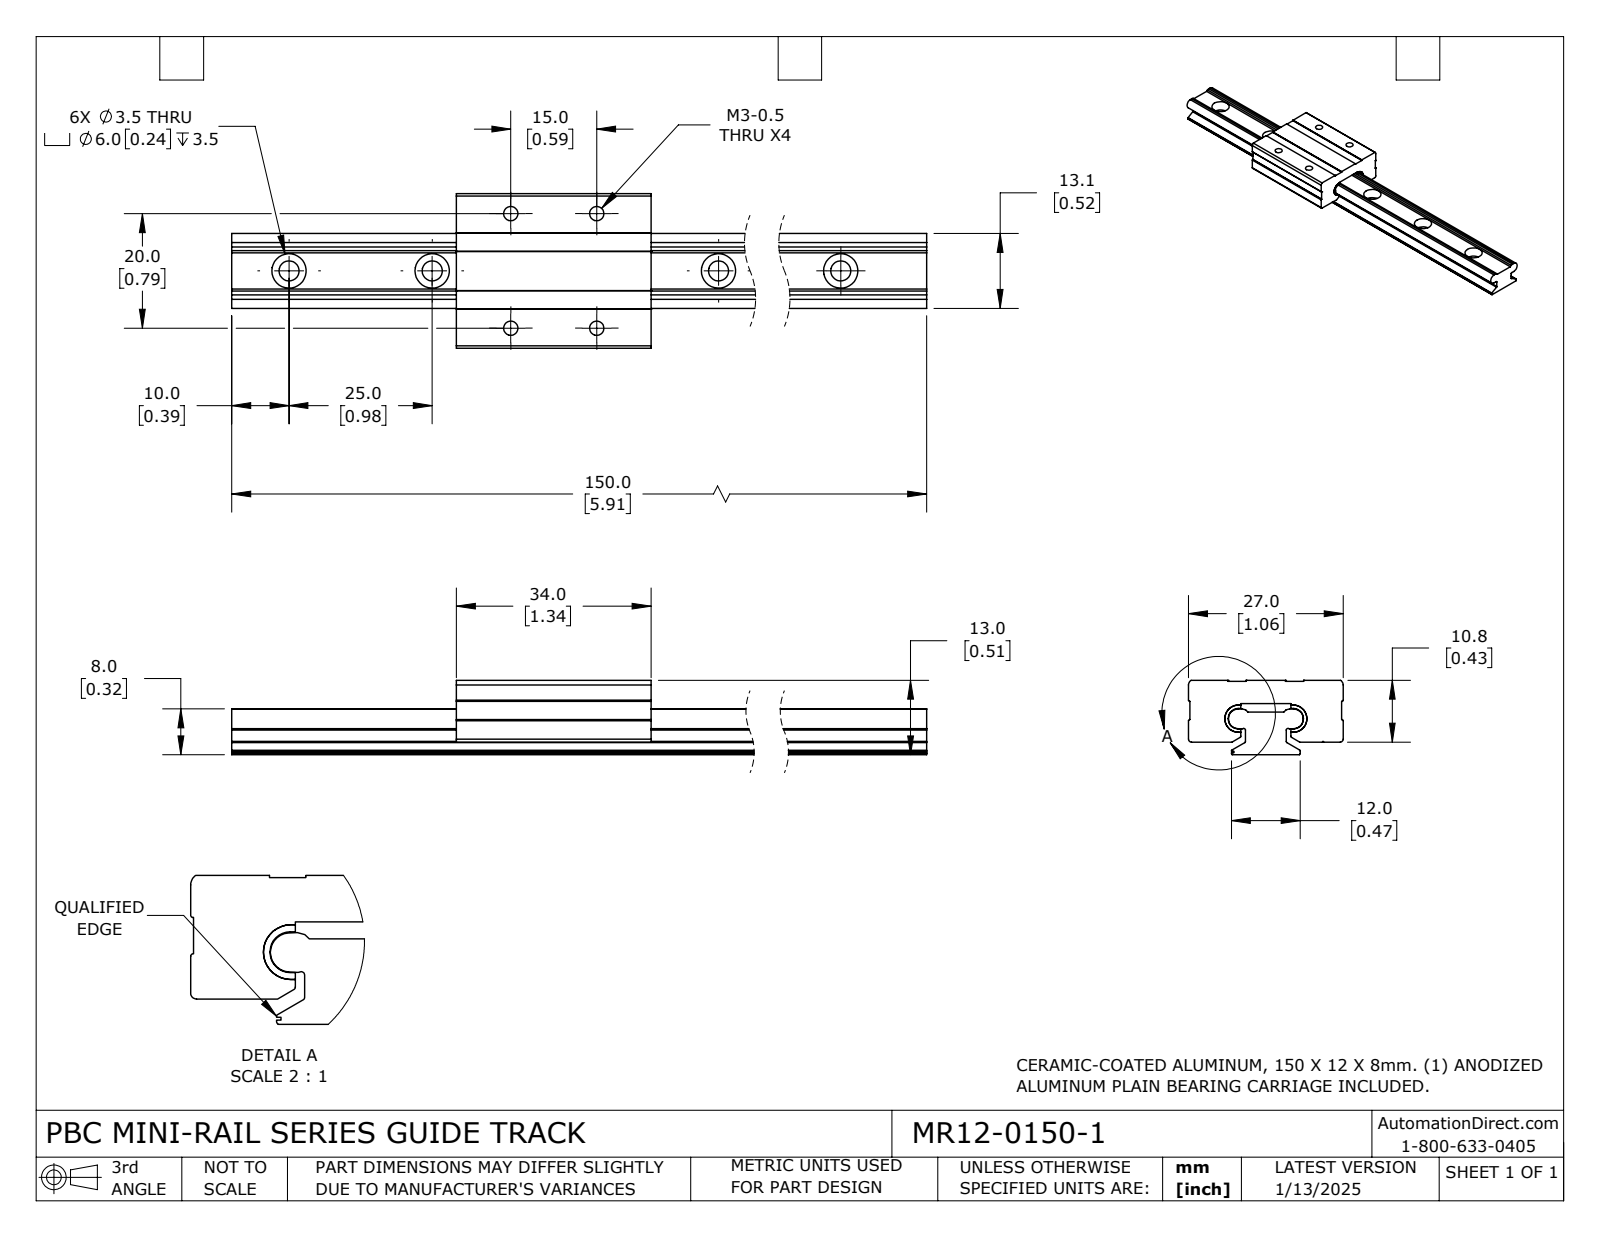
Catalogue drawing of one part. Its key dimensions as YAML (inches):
part_name: "MR12-0150-1_CARRIAGE; MR12-0150-1; MR12-0150-1_RAILS"
step_written_by: "SolidWorks 2023 (CONFIG_CONTROL_DESIGN)"
units: inches
bodies: {solids: 4, faces: 157, planar: 89, cylindrical: 68, other: 0}
overall_size: [5.906, 1.063, 0.512]
volume: 1.099
surface_area: 19.98
round_holes:
  - {diameter: 0.138, count: 6}
  - {diameter: 0.236, count: 6}
  - {diameter: 0.098, count: 4}
partial_cylinders:
  - {radius: 0.01, count: 9}
  - {radius: 0.008, count: 8}
  - {radius: 0.069, count: 4}
  - {radius: 0.011, count: 2}
  - {radius: 0.02, count: 2}
  - {radius: 0.04, count: 2}
  - {radius: 0.067, count: 2}
  - {radius: 0.094, count: 2}
face_to_face_distances: [0.293, 0.512, 0.219, 0.087, 0.206, 0.425, 0.391, 0.672, 0.352, 0.265]
hole_center_spacings: [0.984, 1.969, 2.953, 0.42, 0.591, 0.593, 0.668, 0.787]
